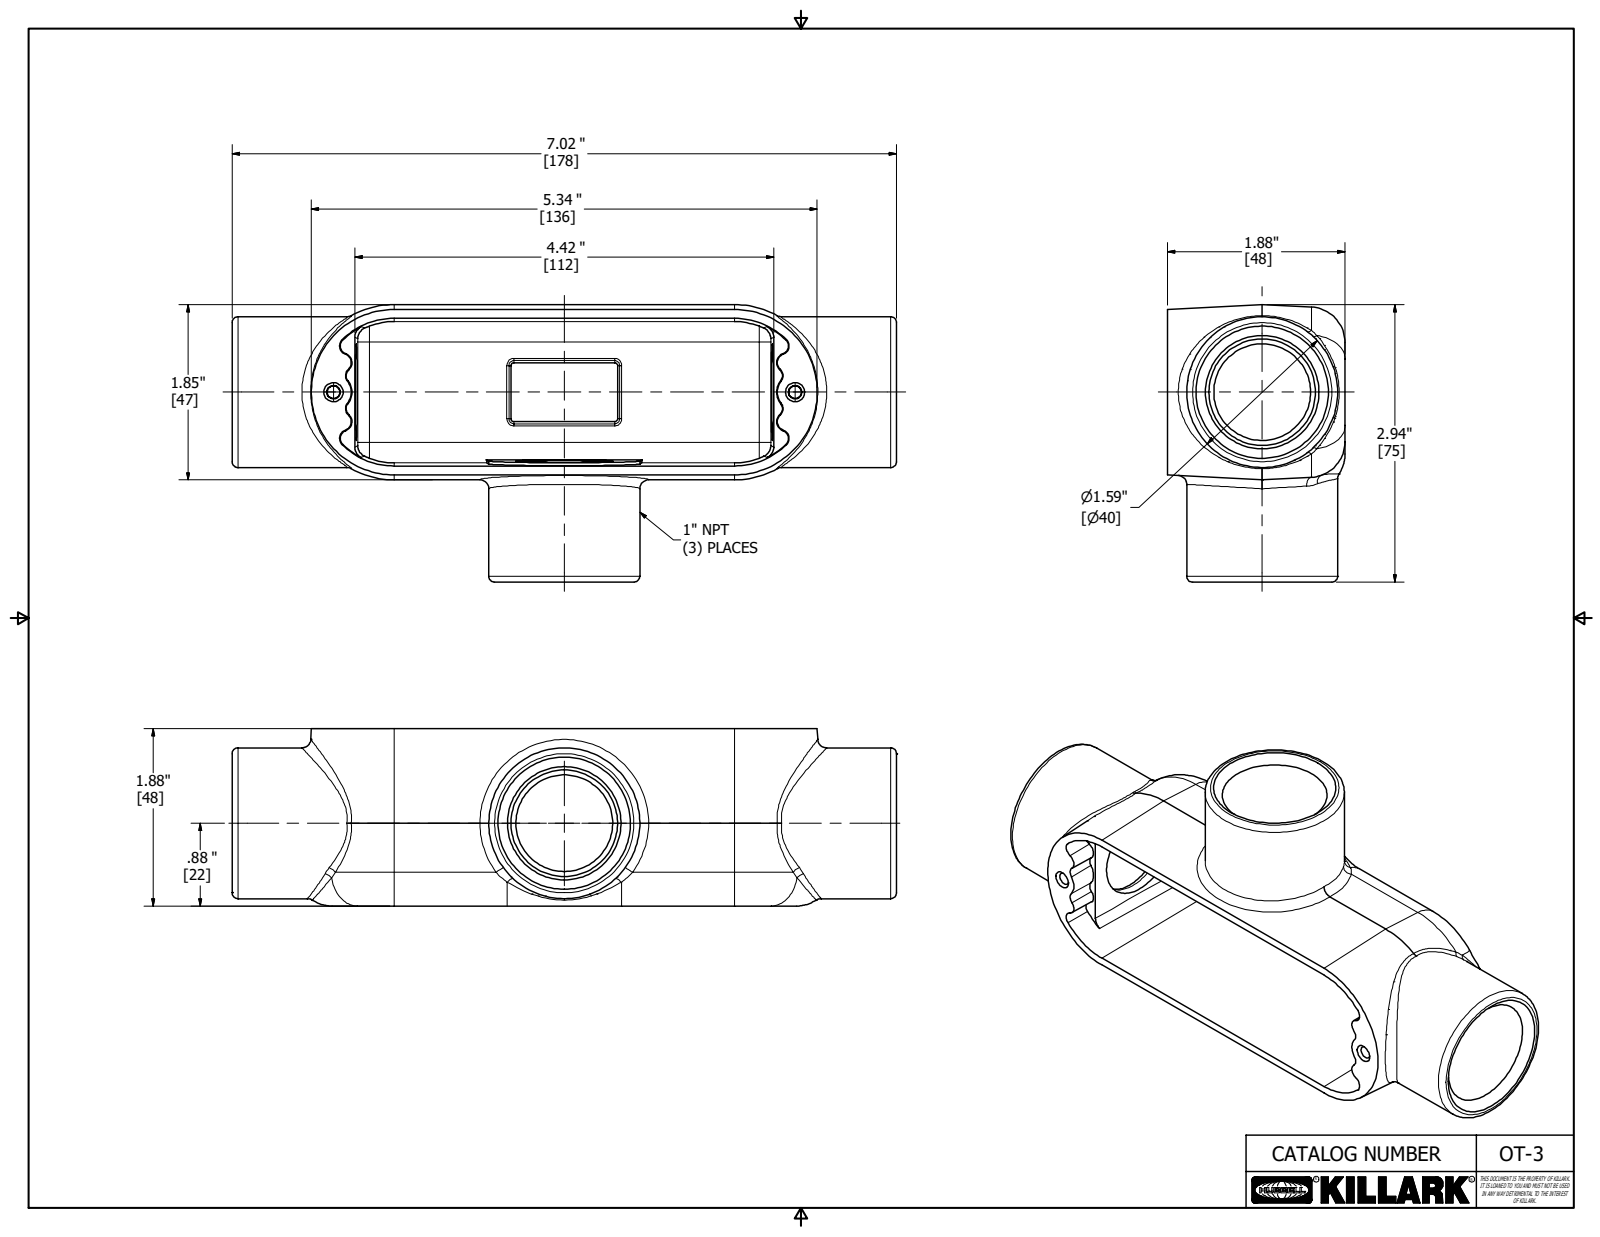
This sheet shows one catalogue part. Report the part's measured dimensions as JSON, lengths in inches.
{"part_name": "11886-1", "step_written_by": "Autodesk Inventor 2018 (AUTOMOTIVE_DESIGN)", "units": "inches", "bodies": {"solids": 1, "faces": 135, "planar": 32, "cylindrical": 18, "other": 85}, "overall_size": [7.017, 2.936, 1.875], "volume_in3": 6.608, "surface_area_in2": 82.11, "round_holes": [[1.022, 2]], "round_bosses_or_shafts": [[1.594, 2]], "partial_cylinders_radius": [[0.031, 4], [0.125, 2], [0.219, 2], [0.375, 2]], "face_to_face_distances": [0.094, 0.031, 1.853, 1.875, 1.781, 1.852, 0.125, 1.75, 0.031, 0.063]}
